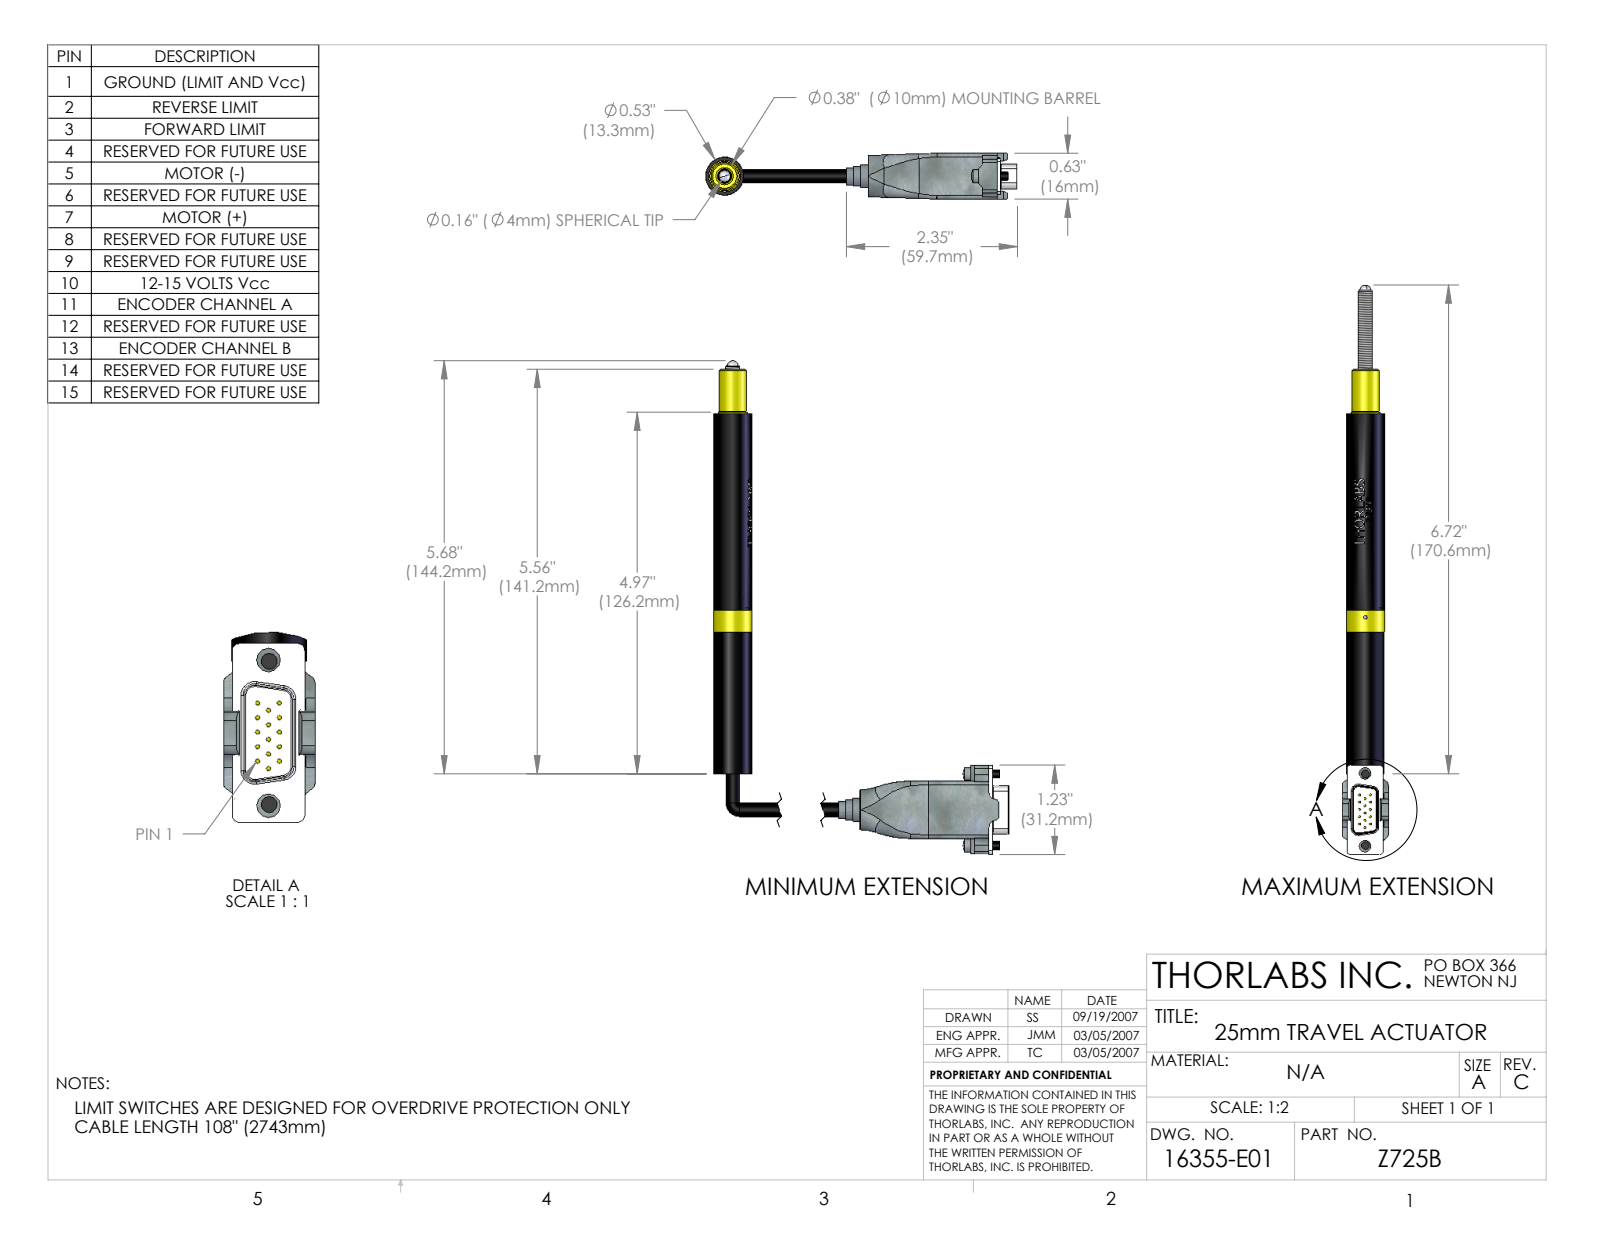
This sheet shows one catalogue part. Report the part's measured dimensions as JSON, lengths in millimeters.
{"part_name": "16355-E0W", "step_written_by": "SolidWorks 2007 (AUTOMOTIVE_DESIGN)", "units": "millimeters", "bodies": {"solids": 7, "faces": 649, "planar": 230, "cylindrical": 307, "other": 112}, "overall_size": [172.4, 109, 16], "volume_mm3": 23430, "surface_area_mm2": 26160, "round_holes": [[0.5, 15], [4.1, 2], [1.3, 1], [4, 1], [4.6, 1], [4.8, 1], [5, 1], [5.1, 1], [9.4, 1], [9.5, 1], [11, 1], [12.2, 1]], "round_bosses_or_shafts": [[0.8, 15], [4.4, 2], [2.8, 2], [14, 1], [13.3, 1], [12.8, 1], [11.2, 1], [10.2, 1]], "partial_cylinders_radius": [[1.6, 9], [0.3, 8], [0.4, 8], [1, 8], [0.5, 6], [1.3, 6], [1.5, 6], [0.1, 4]], "face_to_face_distances": [0.5, 16, 20.1, 2.2, 4.4, 13.8, 0.9, 5.6, 1.2, 2.5], "hole_center_spacings": [2.3, 4.3, 2.5, 6.6, 5.1, 4.6, 6.4, 7.6]}
